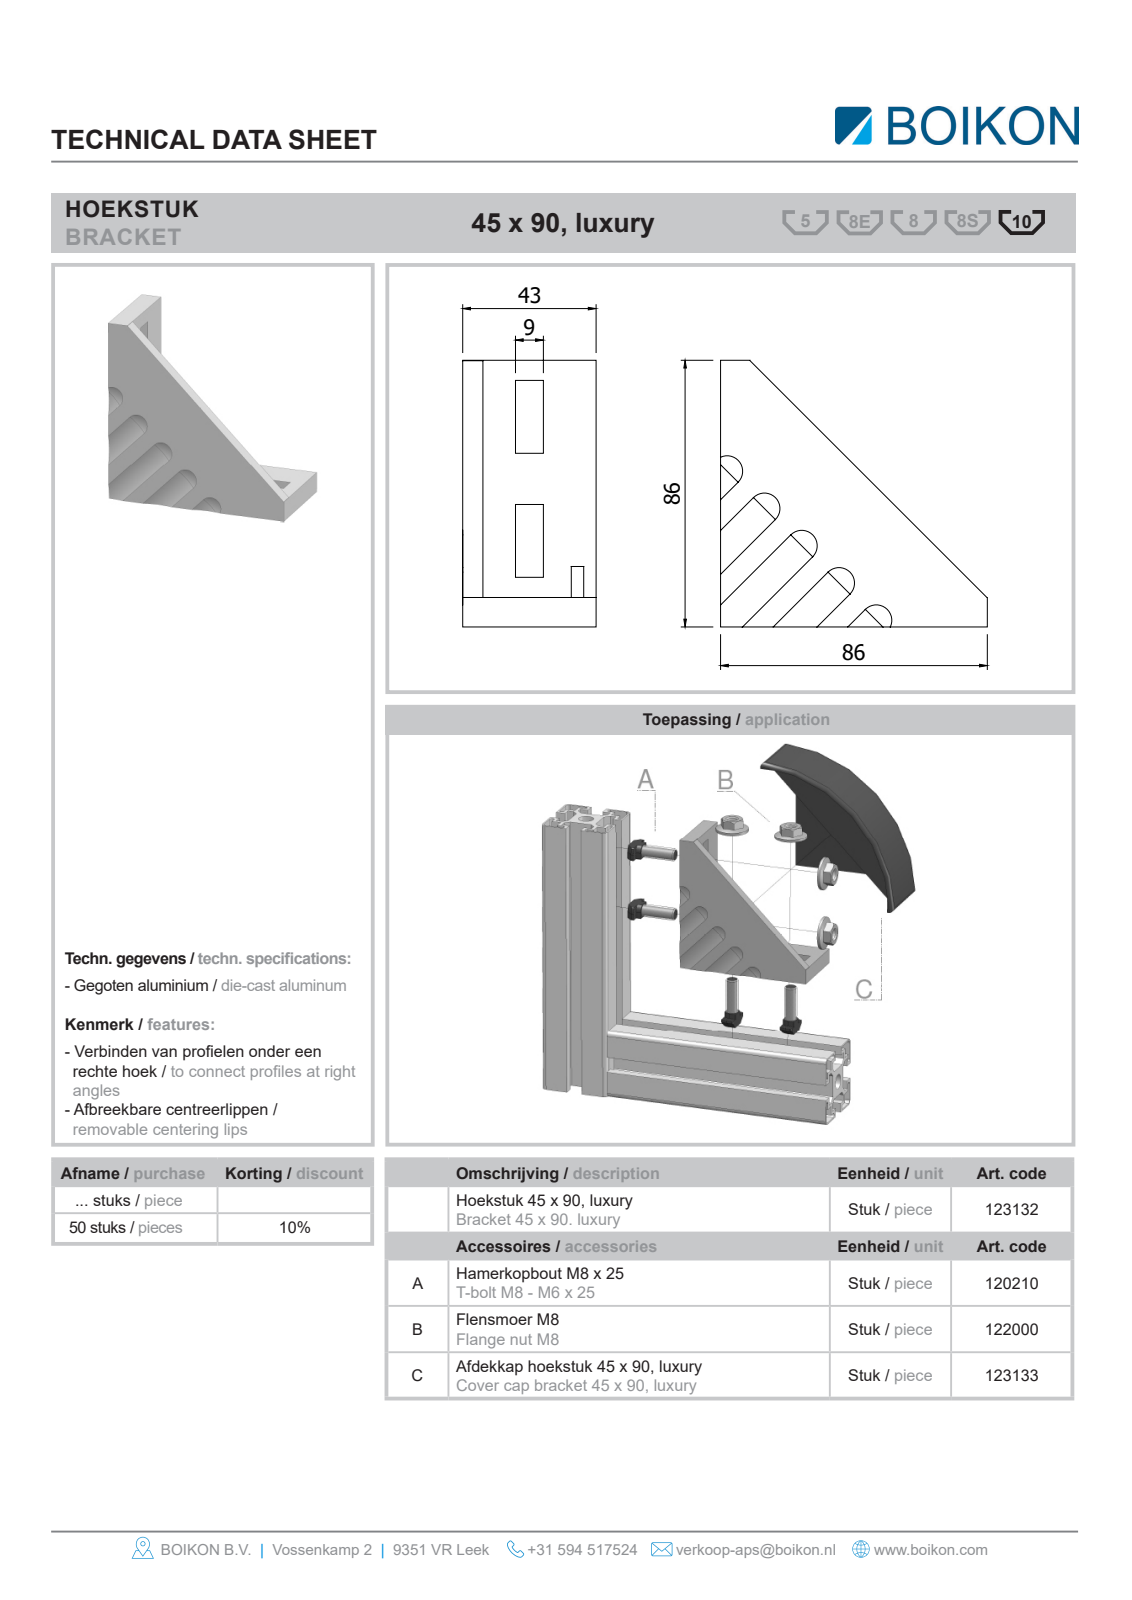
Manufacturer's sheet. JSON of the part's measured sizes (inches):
{"part_name": "Root; 123132HOEKSTUK 45 x90 LUXURYBOIKON; 122000Flensmoer M8BOIKON; 120210Hamerkopbout M8x25BOIKON (+1 more)", "step_written_by": "HiCAD 2013 1802.4 Build 509 (AUTOMOTIVE_DESIGN)", "units": "inches", "bodies": {"solids": 10, "faces": 406, "planar": 284, "cylindrical": 66, "other": 56}, "overall_size": [4.002, 4.002, 1.693], "volume_in3": 8.062, "surface_area_in2": 89.24, "round_holes": [[0.315, 4]], "round_bosses_or_shafts": [[0.827, 4], [0.255, 4]], "partial_cylinders_radius": [[0.039, 16], [0.512, 10], [0.016, 8], [0.197, 4], [0.382, 4], [0.106, 2], [3.386, 1], [3.543, 1]], "face_to_face_distances": [0.374, 1.693, 0.157, 1.535, 0.256, 1.28, 1.437, 1.575, 0.669, 1.024], "hole_center_spacings": [1.575]}
